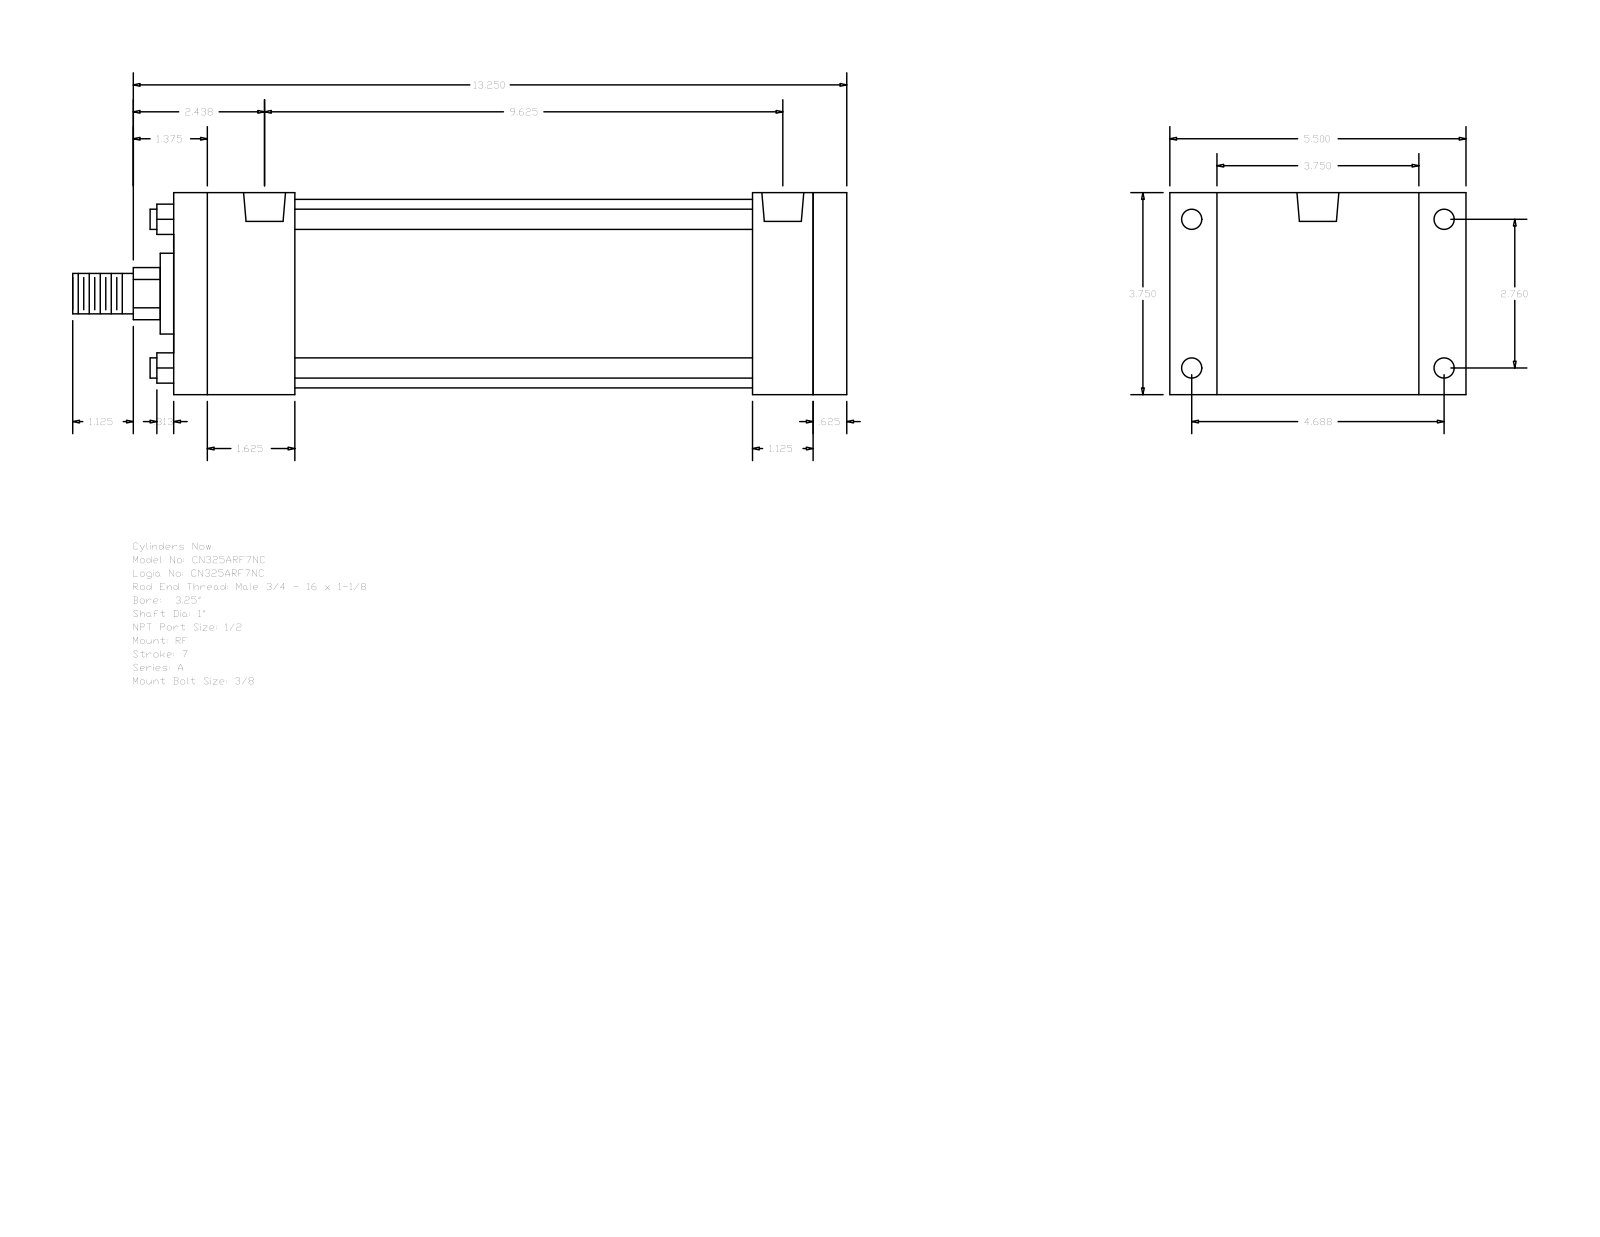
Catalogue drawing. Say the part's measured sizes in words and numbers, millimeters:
The part is named "A_RF__0325_1". Its 3-D file was written by "GSSL Pune (CONFIG_CONTROL_DESIGN)". It is 0 solids with 92 faces: 64 planar, 28 cylindrical and 0 other. Overall it measures 365.12 by 139.7 by 95.25 millimeters. Round holes: 4 of diameter 8.73, 4 of diameter 9.53, 2 of diameter 19.77. Round bosses or shafts: 4 of diameter 9.53, 1 of diameter 88.9, 1 of diameter 38.1, 1 of diameter 25.4, 1 of diameter 19.05. Partial cylindrical surfaces (rounded edges, fillets, slot ends): 1 of radius 12.29. The main face-to-face distances are 95.24, 317.5, 301.63, 15.87, 22.23, 117.47, 273.05, 28.58, 44.45, 57.15. The hole center spacings are 3.18, 70.1, 119.06, 138.16, 238.12, 241.3, 244.48.
